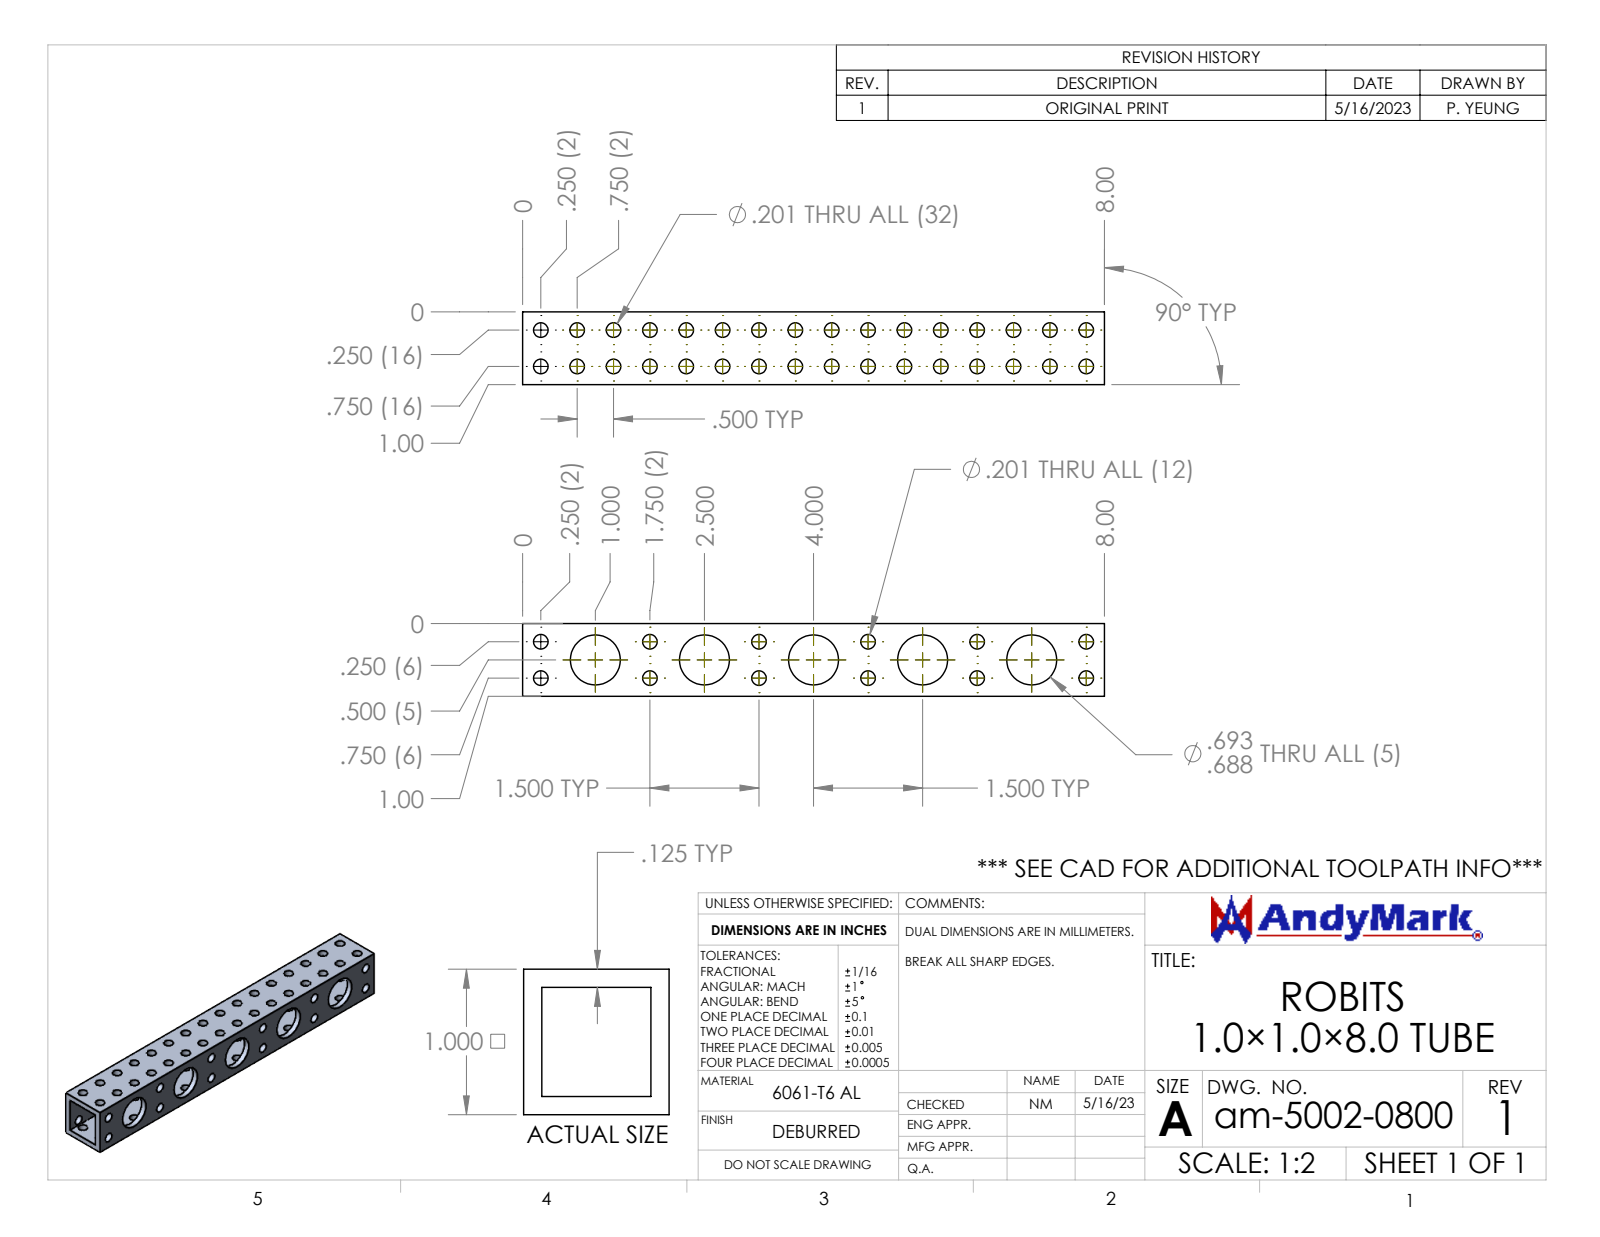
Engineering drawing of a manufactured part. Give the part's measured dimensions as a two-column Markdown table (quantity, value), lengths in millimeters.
| quantity | value |
| --- | --- |
| part name | am-5002-0800 RoBits 1.0x1.0x8.0 Tube |
| STEP written by | SolidWorks 2022 (CONFIG_CONTROL_DESIGN) |
| units | millimeters |
| bodies | 1 solid, 206 faces (10 planar, 196 cylindrical, 0 other) |
| overall size | 203.2 × 25.4 × 25.4 |
| volume | 27 120 mm³ |
| surface area | 39 920 mm² |
| round holes (diameter × count) | 5.1 × 44, 17.4 × 5 |
| main face-to-face distances | 25.4, 3.2, 22.2, 19.1, 22.2, 3.2, 203.2 |
| hole center spacings | 12.7, 38.1, 40.2, 76.2, 18, 25.4, 28.4, 77.2 |
